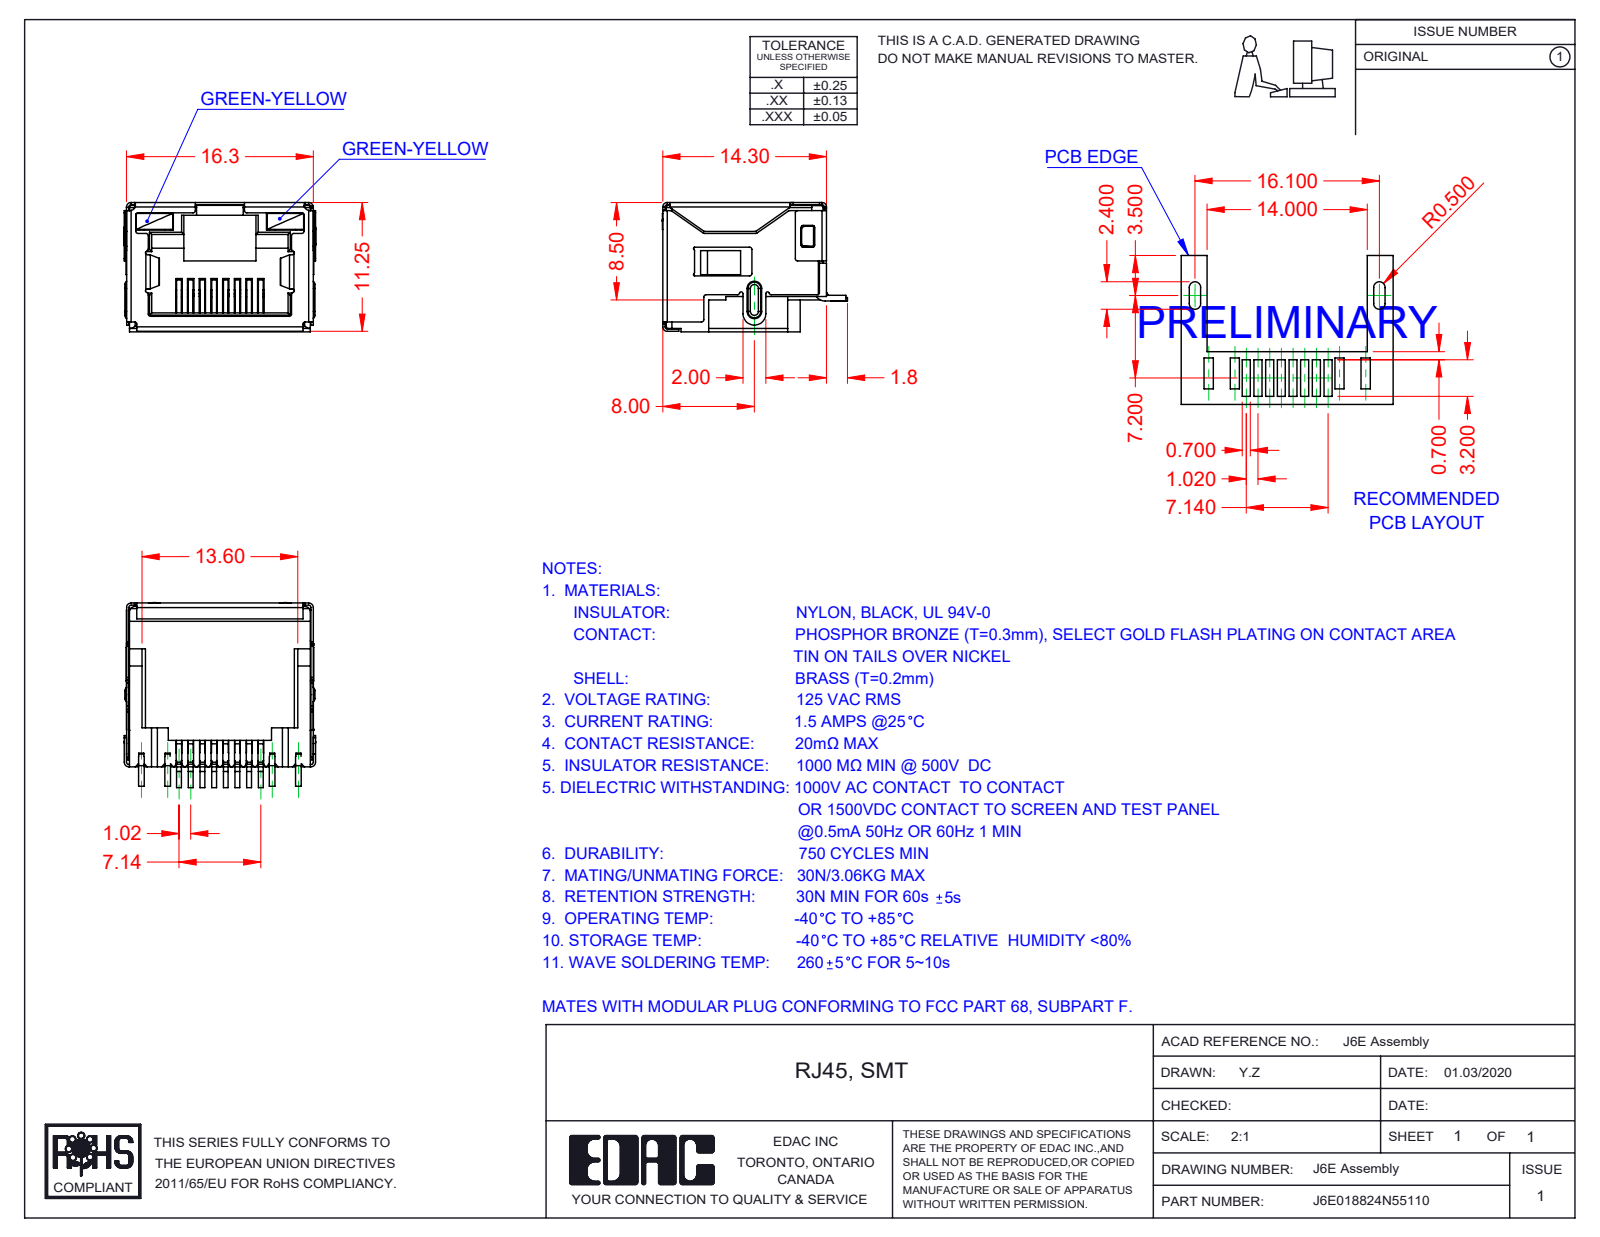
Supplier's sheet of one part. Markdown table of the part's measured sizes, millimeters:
| quantity | value |
| --- | --- |
| part name | J6E018824N55110; 6E Contacts; 6E LED RH_5-Green-Yellow; 6E Shield_LED (+2 more) |
| STEP written by | SolidWorks 2016 (CONFIG_CONTROL_DESIGN) |
| units | millimeters |
| bodies | 12 solids, 1500 faces (1099 planar, 351 cylindrical, 50 other) |
| overall size | 16.75 × 16.15 × 11.3 |
| volume | 1 109 mm³ |
| surface area | 4 045 mm² |
| partial cylindrical surfaces (radius × count) | 0.2 × 82, 0.25 × 17, 0.4 × 13, 0.5 × 13, 0.1 × 10, 0.15 × 7, 0.3 × 4, 1 × 3 |
| main face-to-face distances | 11.05, 16.05, 16.1, 15.85, 11.1, 11.3, 2.4, 0.7, 9.85, 0.49 |
